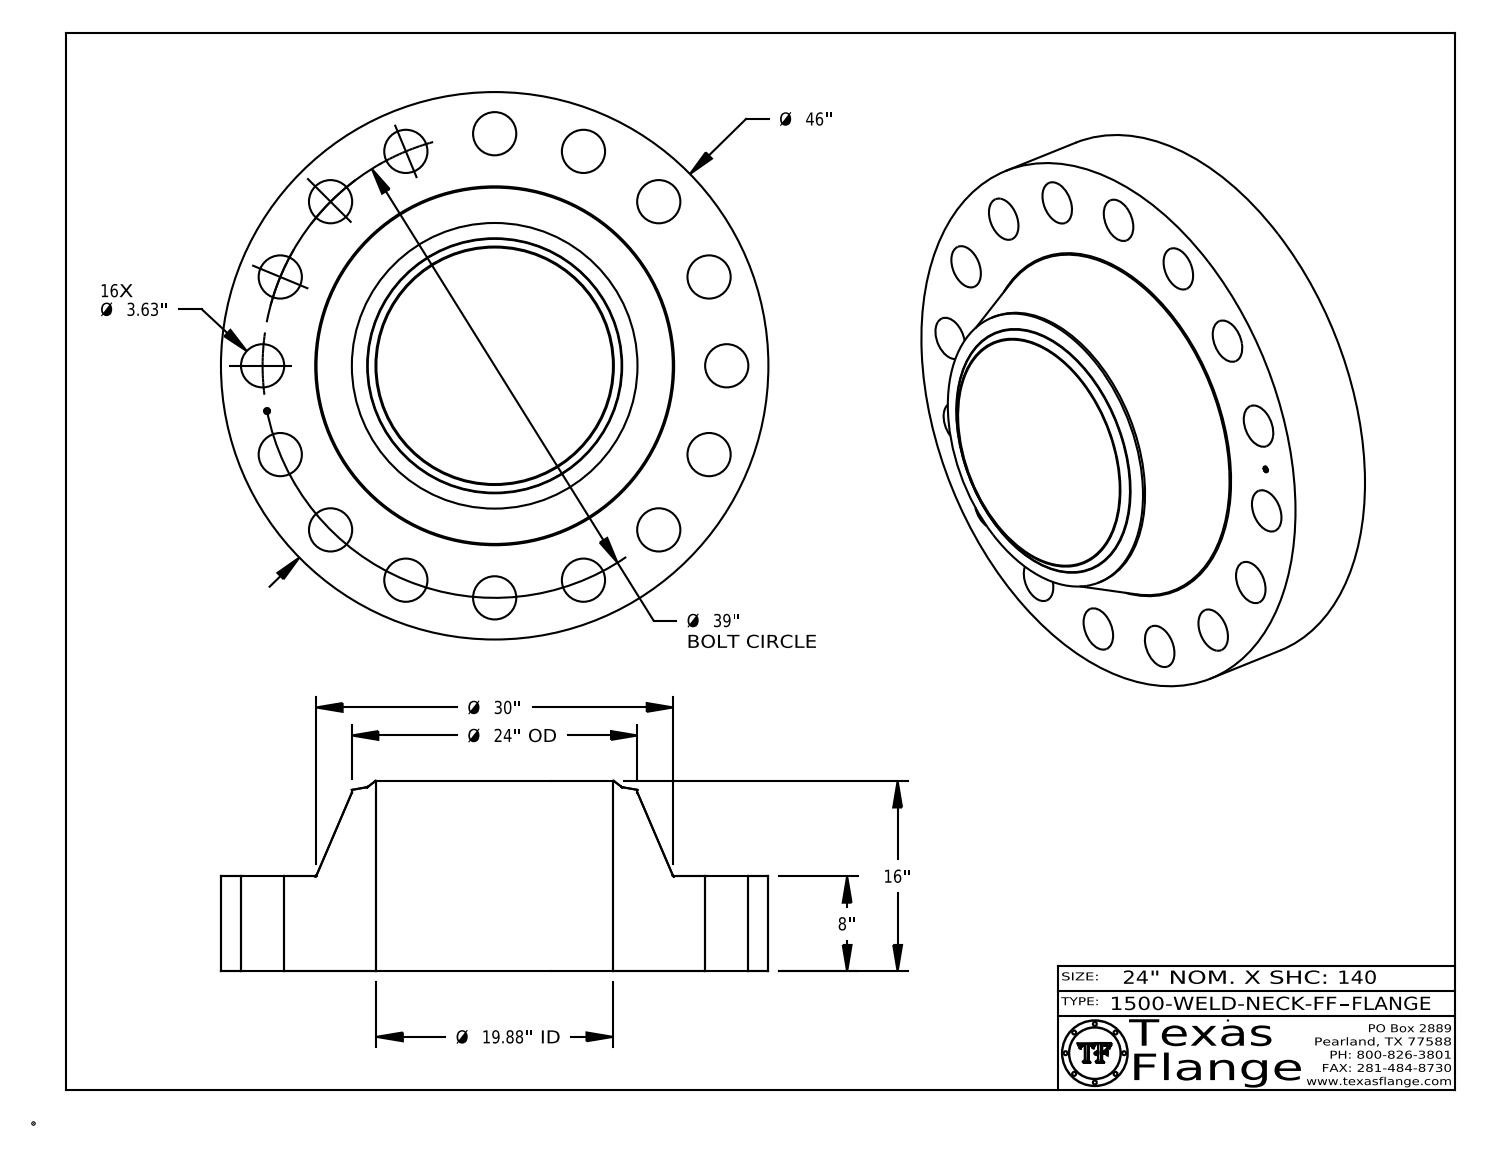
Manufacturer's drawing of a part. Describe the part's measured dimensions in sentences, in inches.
The part is named "1500-WELD-NECK-FF". Its 3-D file was written by "CATIA V5 STEP AP214 (AUTOMOTIVE_DESIGN)". It is 1 solid with 436 faces: 368 planar, 58 cylindrical and 10 other. Overall it measures 46 by 46 by 16 inches. Its volume is 11 415 cubic inches and its surface area 6 409 square inches. Round holes: 16 of diameter 3.63, 1 of diameter 0.495, 1 of diameter 19.876. Round bosses or shafts: 8 of diameter 0.03, 1 of diameter 46, 1 of diameter 24, 1 of diameter 0.39. The main face-to-face distances are 8, 16, 7.985, 0.015, 8.015, 0.148, 0.145, 0.027, 0.096, 0.123. The hole center spacings are 19.5, 21.667, 27.577, 38.251, 14.925, 36.031, 7.608, 7.609.
